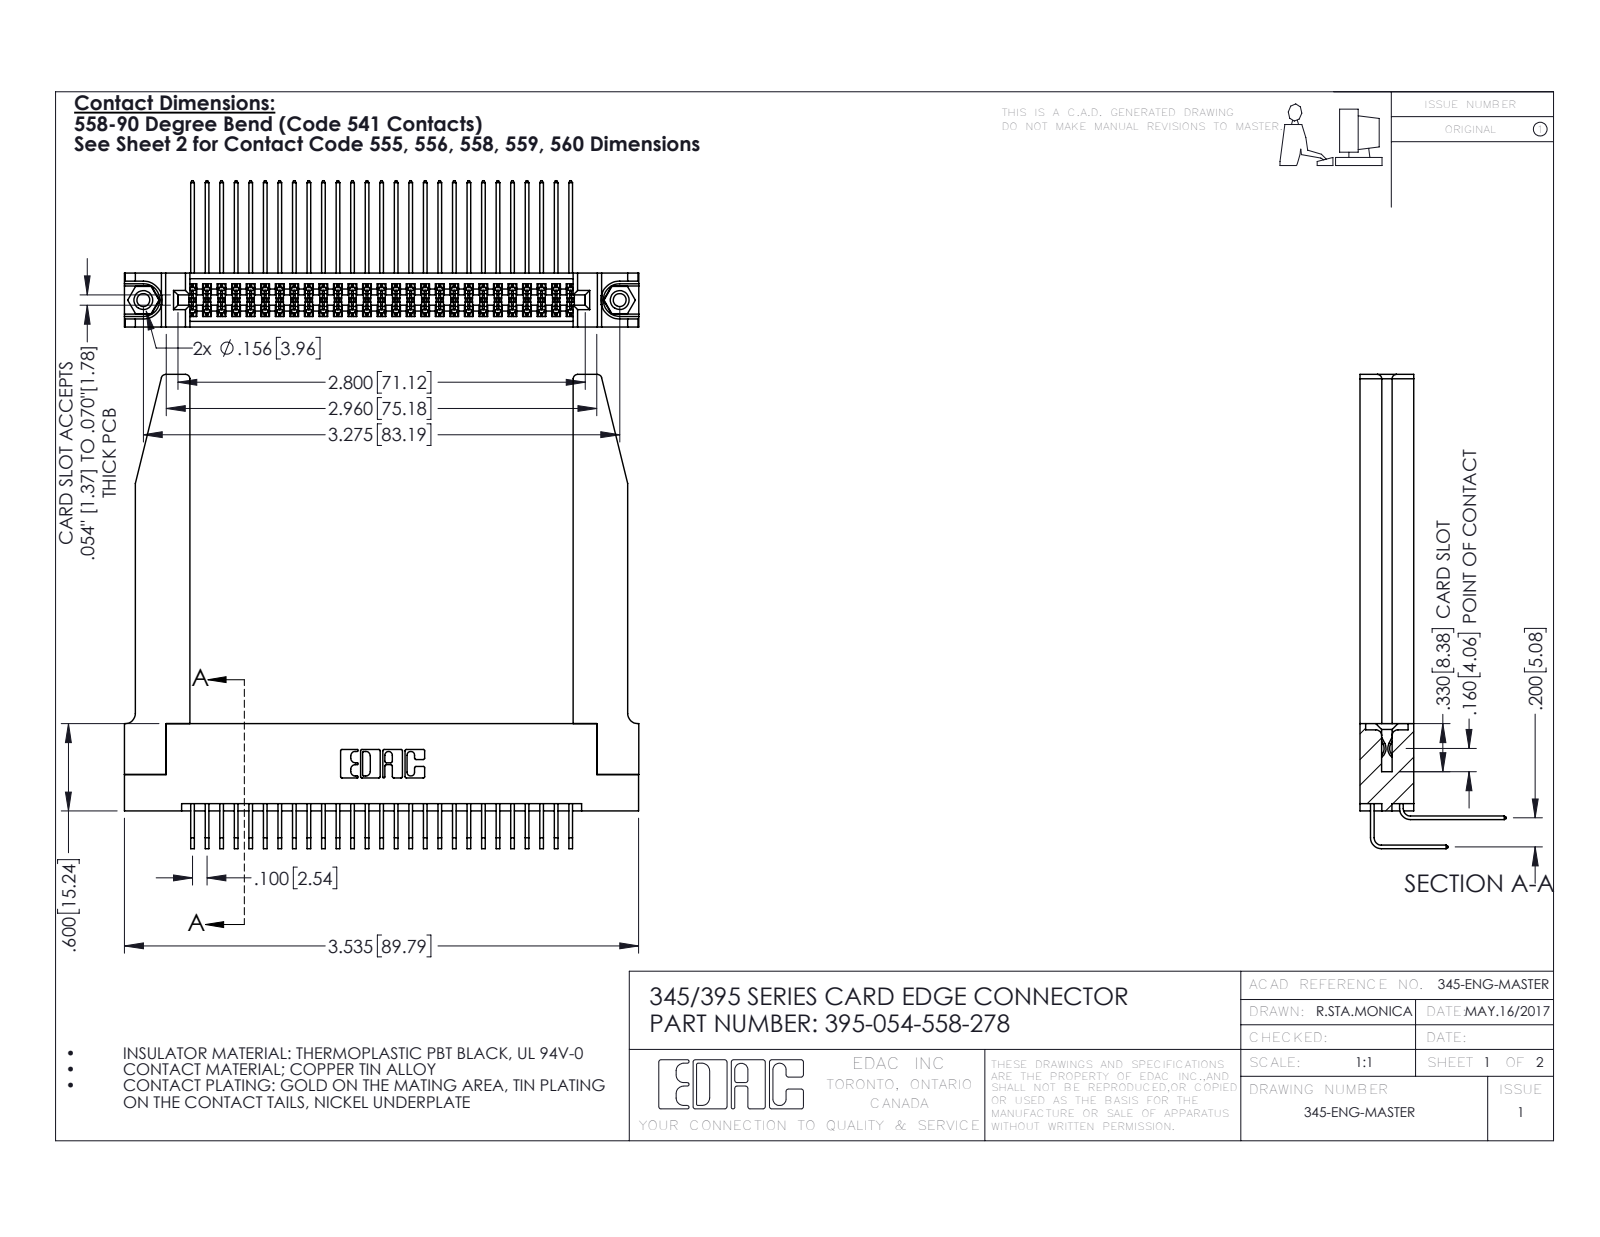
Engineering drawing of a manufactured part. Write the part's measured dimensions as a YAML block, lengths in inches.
part_name: "345-250-001_345-250-001-102; 345-292-001_558 Tail - 2; 395-054-558-278; 345-292-001_558 559 Tail - 1 (+2 more)"
step_written_by: "SolidWorks 2016 (CONFIG_CONTROL_DESIGN)"
units: inches
bodies: {solids: 59, faces: 3168, planar: 2112, cylindrical: 1004, other: 52}
overall_size: [3.536, 3.259, 1.005]
volume: 1.017
surface_area: 32.8
round_holes:
  - {diameter: 0.089, count: 2}
  - {diameter: 0.125, count: 2}
  - {diameter: 0.156, count: 2}
  - {diameter: 0.064, count: 1}
round_bosses_or_shafts:
  - {diameter: 0.155, count: 2}
partial_cylinders:
  - {radius: 0.006, count: 82}
  - {radius: 0.01, count: 22}
  - {radius: 0.03, count: 8}
  - {radius: 0.007, count: 6}
  - {radius: 0.031, count: 6}
  - {radius: 0.026, count: 3}
  - {radius: 0.014, count: 2}
  - {radius: 0.019, count: 2}
face_to_face_distances: [0.37, 0.072, 0.298, 0.2, 0.098, 0.272, 0.025, 0.225, 0.148, 0.15]
hole_center_spacings: [0.27, 3.04, 3.275]
